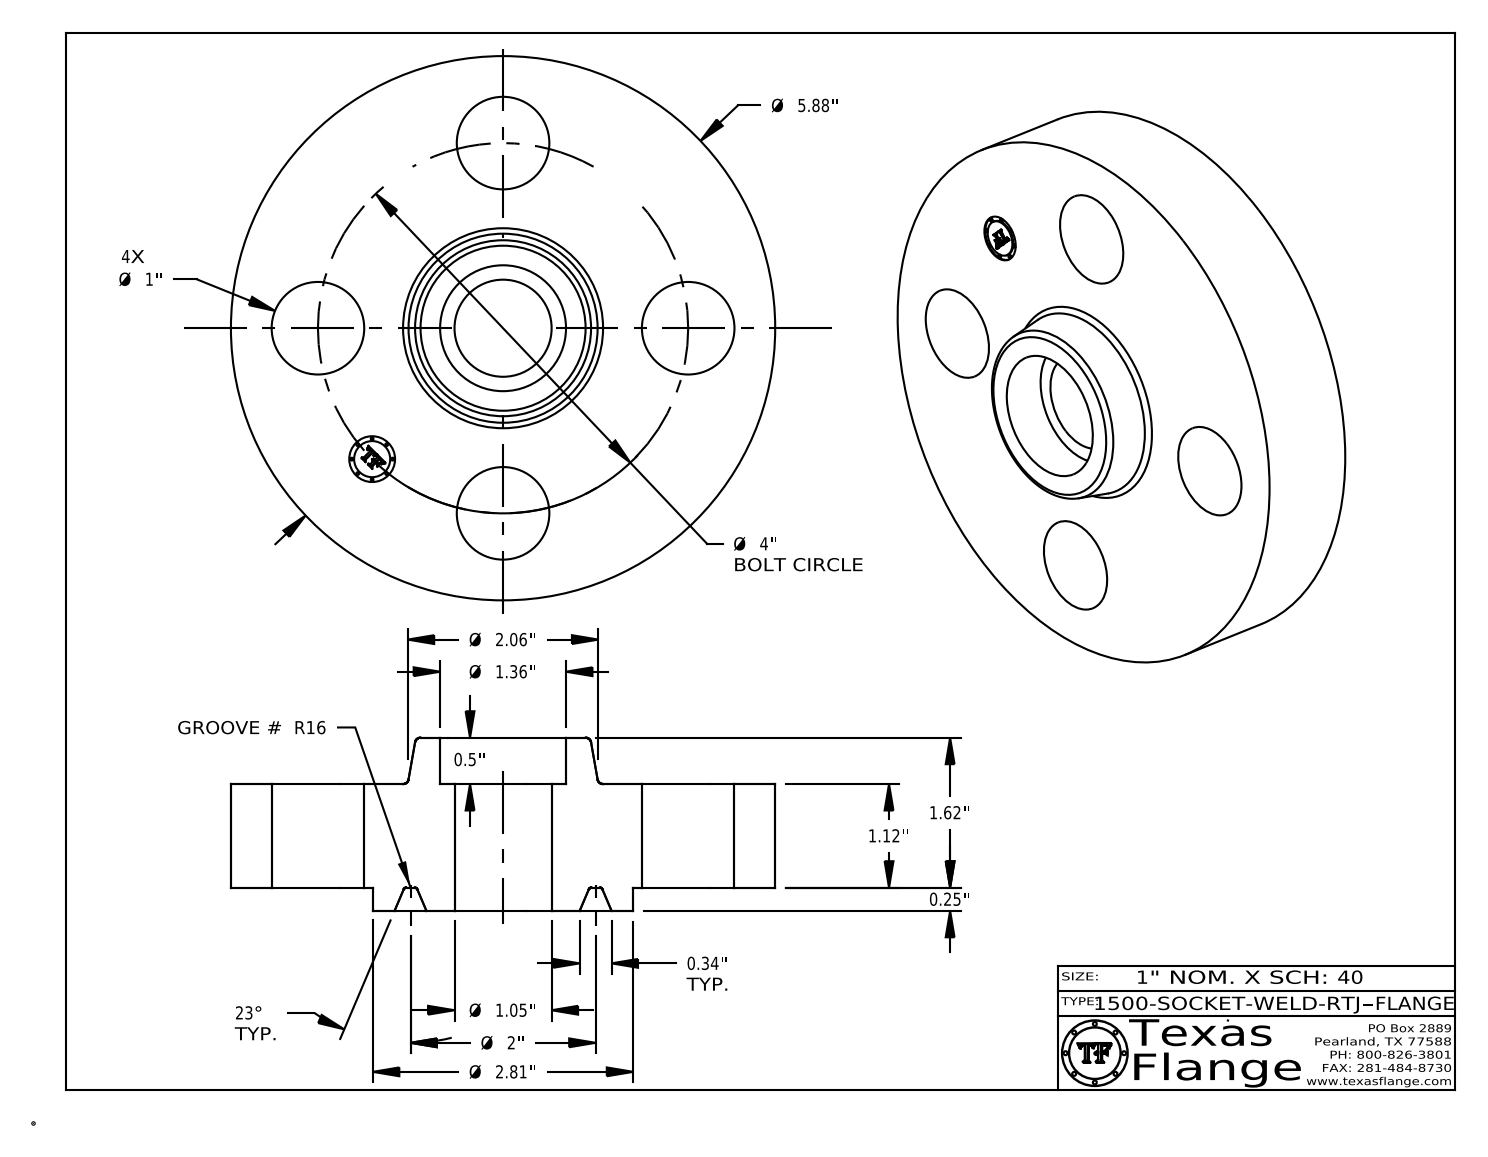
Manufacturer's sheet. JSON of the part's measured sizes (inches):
{"part_name": "1500-SOCKET-WELD-RTJ", "step_written_by": "CATIA V5 STEP AP214 (AUTOMOTIVE_DESIGN)", "units": "inches", "bodies": {"solids": 1, "faces": 422, "planar": 372, "cylindrical": 36, "other": 14}, "overall_size": [5.88, 5.88, 1.87], "volume_in3": 27.69, "surface_area_in2": 94.42, "round_holes": [[1, 4], [0.495, 1], [1.049, 1], [1.36, 1]], "round_bosses_or_shafts": [[0.03, 8], [5.88, 1], [2.813, 1], [0.39, 1]], "face_to_face_distances": [1.12, 0.25, 1.37, 1.87, 1.62, 0.5, 0.015, 1.355, 1.105, 0.515], "hole_center_spacings": [2, 2.828, 1.531, 3.695, 4]}
